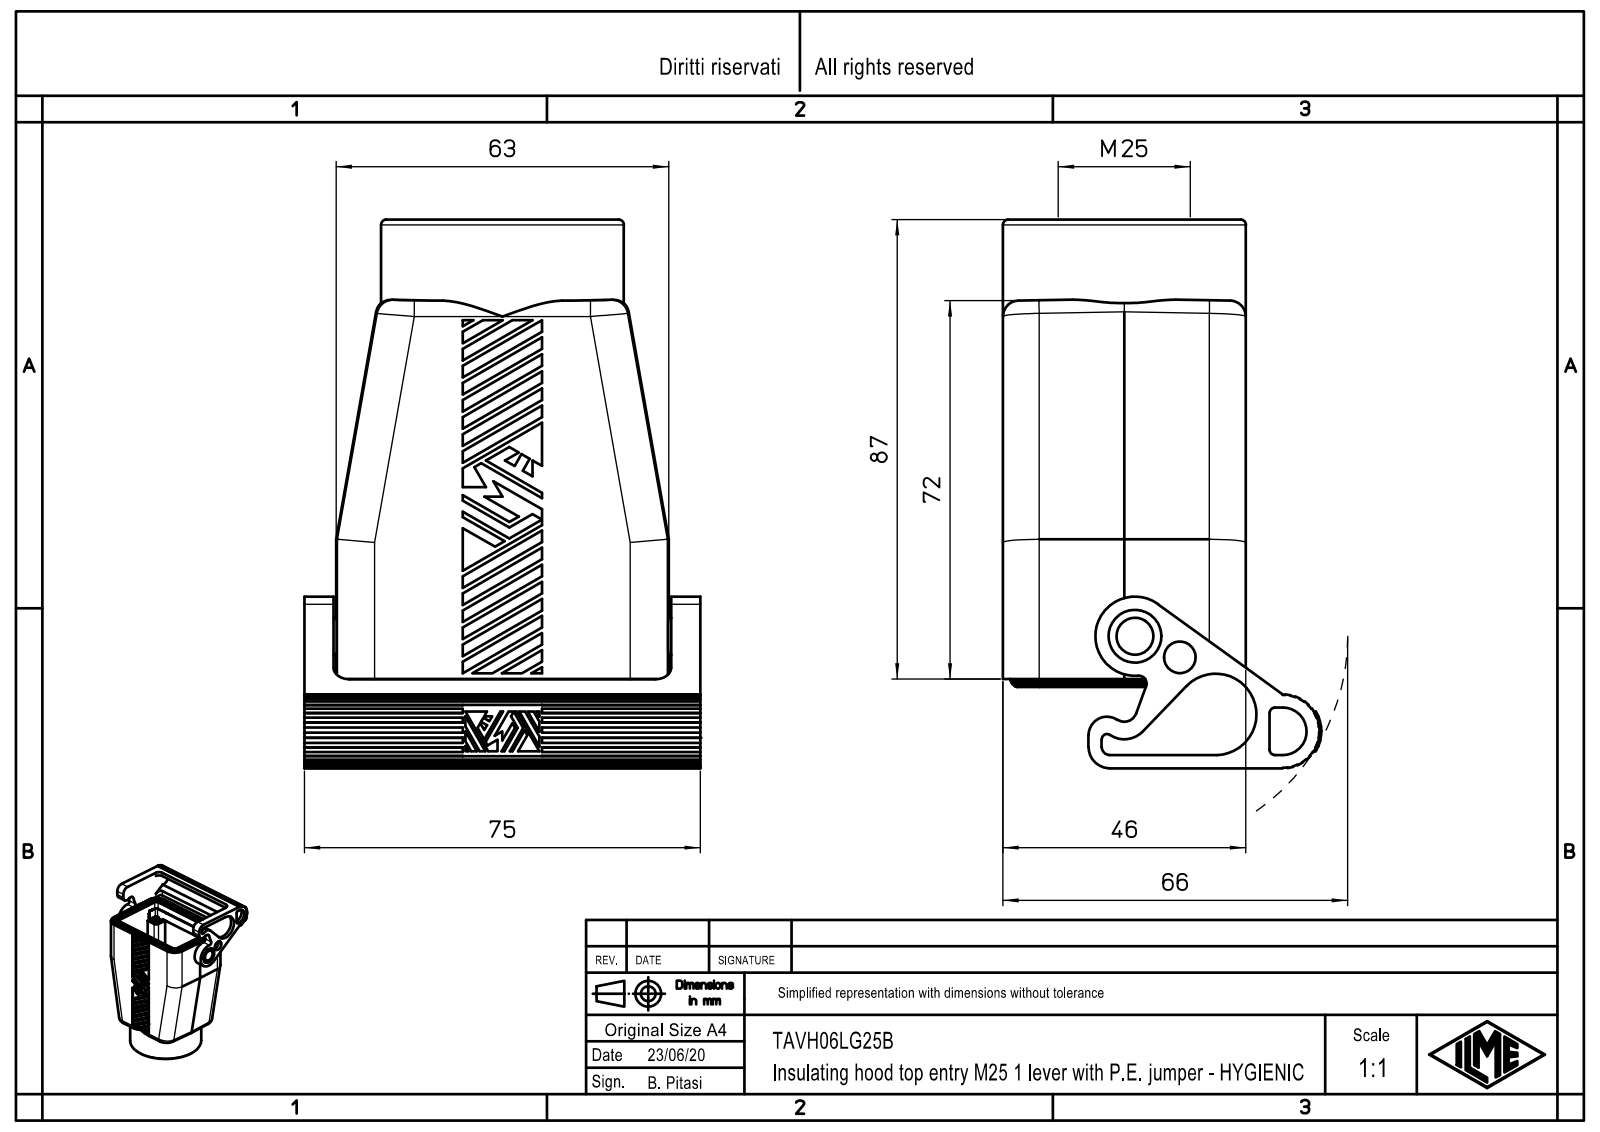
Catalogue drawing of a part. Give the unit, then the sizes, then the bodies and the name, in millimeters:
Units: millimetres
Overall size (bounding box): 103.9 × 75 × 60.3
Round holes (diameter × count): ⌀3.5 ×4, ⌀5.12 ×4, ⌀6.5 ×4, ⌀6 ×1, ⌀10 ×1, ⌀21 ×1, ⌀25 ×1
Round bosses / shafts (diameter × count): ⌀46 ×1, ⌀7 ×1
Partial cylindrical surfaces — rounded edges, fillets, slot ends (radius × count): R1.5 ×14, R7 ×9, R1.81 ×8, R2 ×8, R3 ×8, R1 ×6, R1.3 ×4, R1.6 ×4
Main face-to-face distances: 46, 0.5, 7.98, 45.5, 5.5, 3, 69.5, 20.5, 5.6, 2.5
Hole centre spacings: 25.81, 27, 44, 51.62, 9.39
Volume: 114 659 mm³ · Surface area: 45 657 mm²
Bodies: 1 solid, 680 faces (490 planar, 162 cylindrical, 28 other)
Part name (STEP PRODUCT): TAVH06LG25B
STEP written by: Creo Elements/Direct Modeling 20.1B 02-Apr-2019 (C) Parametric Technology GmbH (AUTOMOTIVE_DESIGN)
